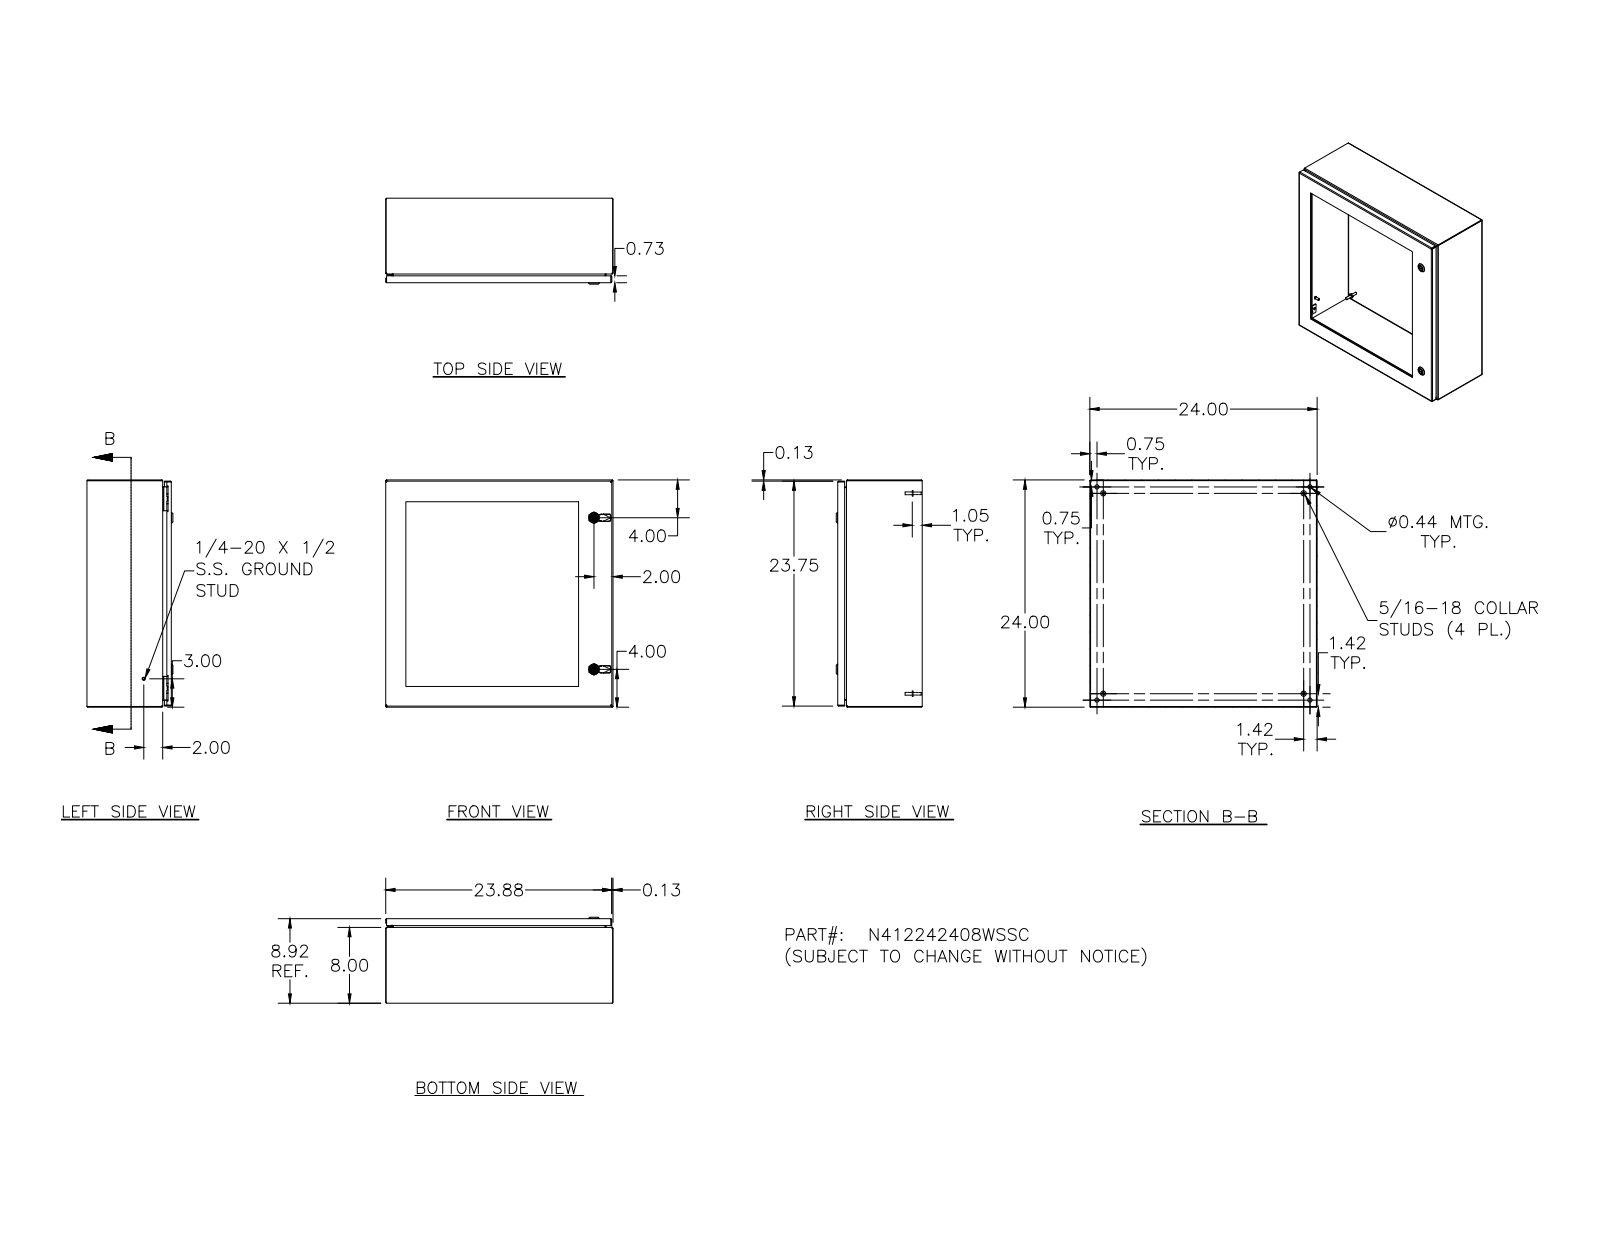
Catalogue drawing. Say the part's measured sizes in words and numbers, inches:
The part is named "N412242408WSSC; N412242408WSSCBKP; N4122424WSSCLID; HFW328176 (+8 more)". Its 3-D file was written by "Autodesk Inventor 2011 (AUTOMOTIVE_DESIGN)". It is 86 solids with 2366 faces: 973 planar, 672 cylindrical and 721 other. Overall it measures 24 by 24 by 9.075 inches. Its volume is 236 cubic inches and its surface area 4 559 square inches. Round holes: 22 of diameter 0.156, 20 of diameter 0.281, 4 of diameter 0.093, 4 of diameter 0.152, 4 of diameter 0.167, 4 of diameter 0.172, 4 of diameter 0.188, 4 of diameter 0.437, 2 of diameter 0.197, 2 of diameter 0.315, 2 of diameter 0.394, 2 of diameter 0.402. Round bosses or shafts: 20 of diameter 0.19, 19 of diameter 0.253, 10 of diameter 0.25, 4 of diameter 0.563, 4 of diameter 0.36, 4 of diameter 0.32, 4 of diameter 0.3, 4 of diameter 0.275. Partial cylindrical surfaces (rounded edges, fillets, slot ends): 34 of radius 0.031, 26 of radius 0.05, 24 of radius 0.105, 18 of radius 0.016, 16 of radius 0.125, 15 of radius 0.02, 8 of radius 0.032, 8 of radius 0.157. The main face-to-face distances are 0.074, 8.843, 23.926, 8.769, 0.25, 8.593, 8.519, 24, 23.852, 8.917. The hole center spacings are 4, 8, 21.132, 12, 19.906, 20, 22.239, 20.75.
